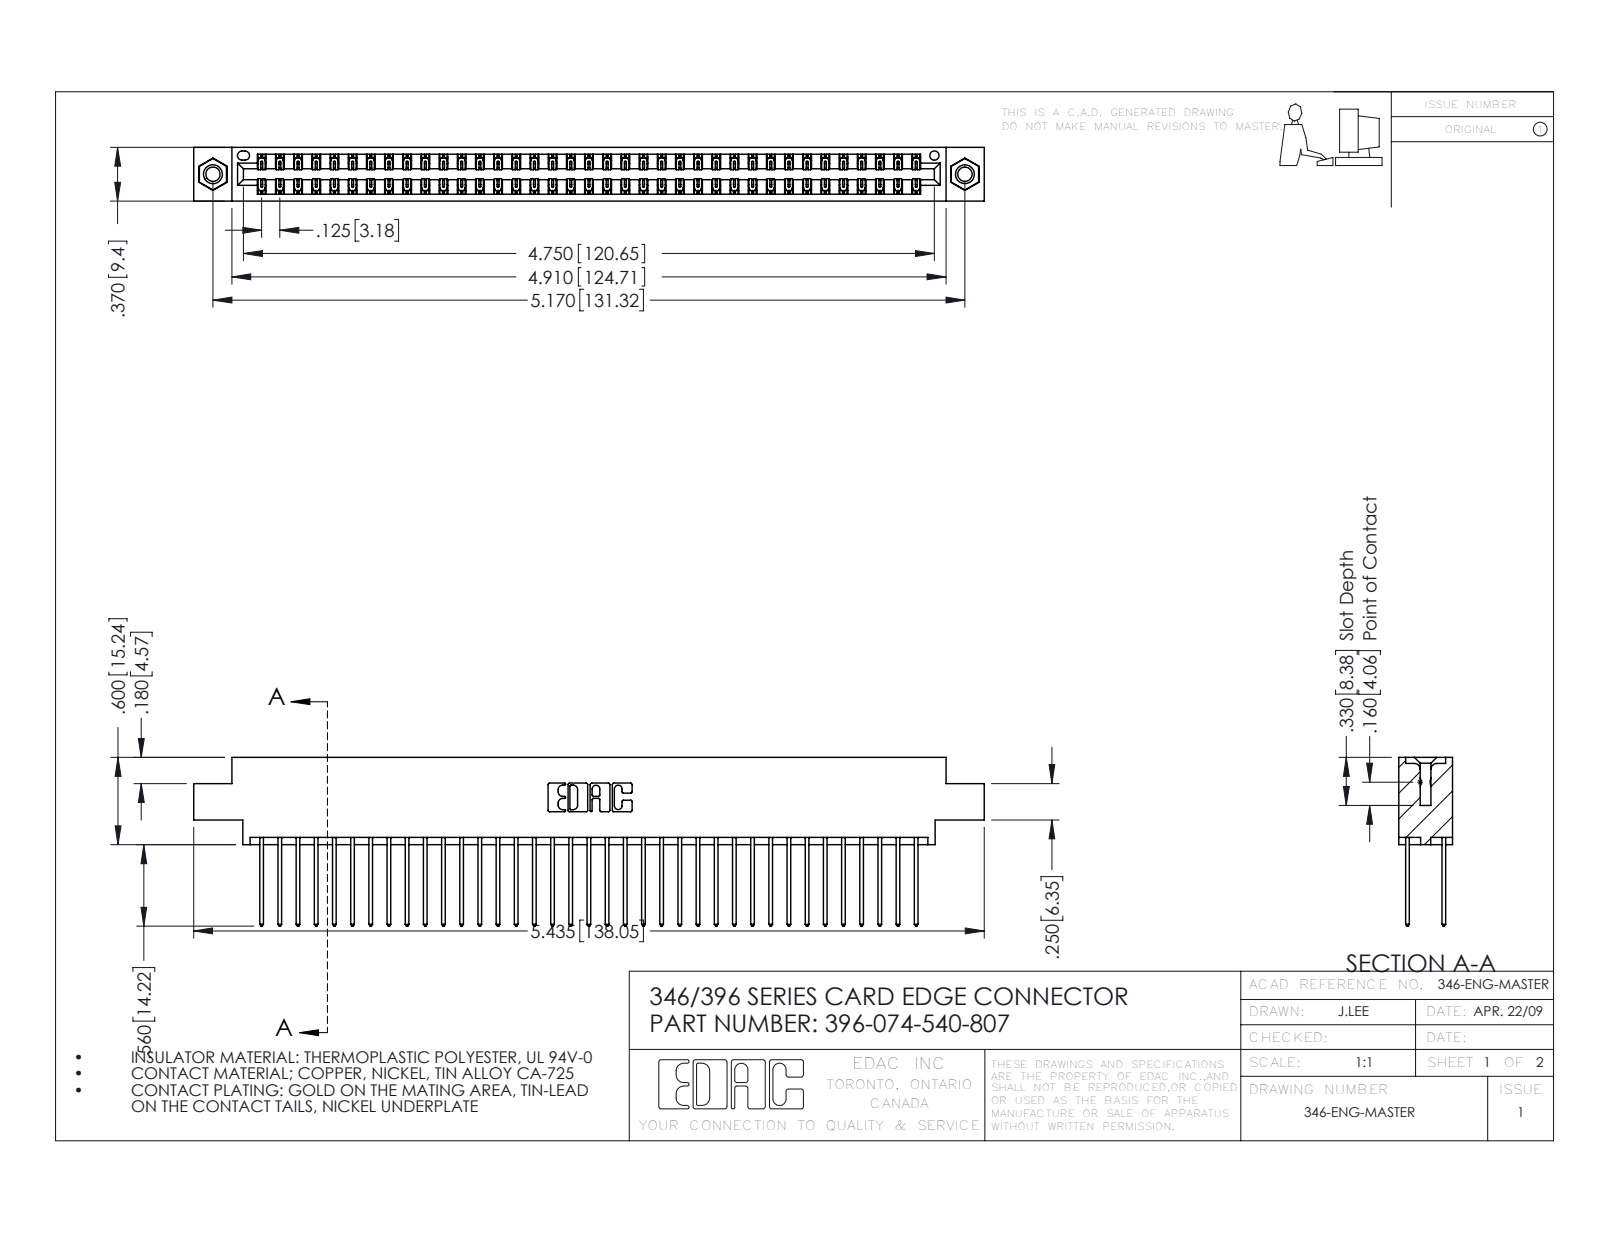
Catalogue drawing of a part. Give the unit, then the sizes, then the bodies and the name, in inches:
Units: inches
Overall size (bounding box): 5.435 × 1.16 × 0.37
Round holes (diameter × count): ⌀0.098 ×2, ⌀0.125 ×2, ⌀0.156 ×2, ⌀0.064 ×1
Round bosses / shafts (diameter × count): ⌀0.155 ×2
Partial cylindrical surfaces — rounded edges, fillets, slot ends (radius × count): R0.006 ×111, R0.01 ×74, R0.01 ×22, R0.007 ×6, R0.031 ×6, R0.026 ×3, R0.014 ×2, R0.022 ×2
Main face-to-face distances: 0.048, 0.322, 0.25, 0.072, 0.298, 0.025, 0.37, 0.275, 0.222, 0.148
Hole centre spacings: 0.246, 4.961, 5.17
Volume: 0.826 in³ · Surface area: 31.1 in²
Bodies: 77 solids, 4034 faces (2702 planar, 1316 cylindrical, 16 other)
Part name (STEP PRODUCT): 396-074-540-807; 346 Part_0.170 Offset - 0.156 Dia-TI; 345-250-001_345-250-005-103; 345-292-001_345-293-140
STEP written by: SolidWorks 2016 (CONFIG_CONTROL_DESIGN)
